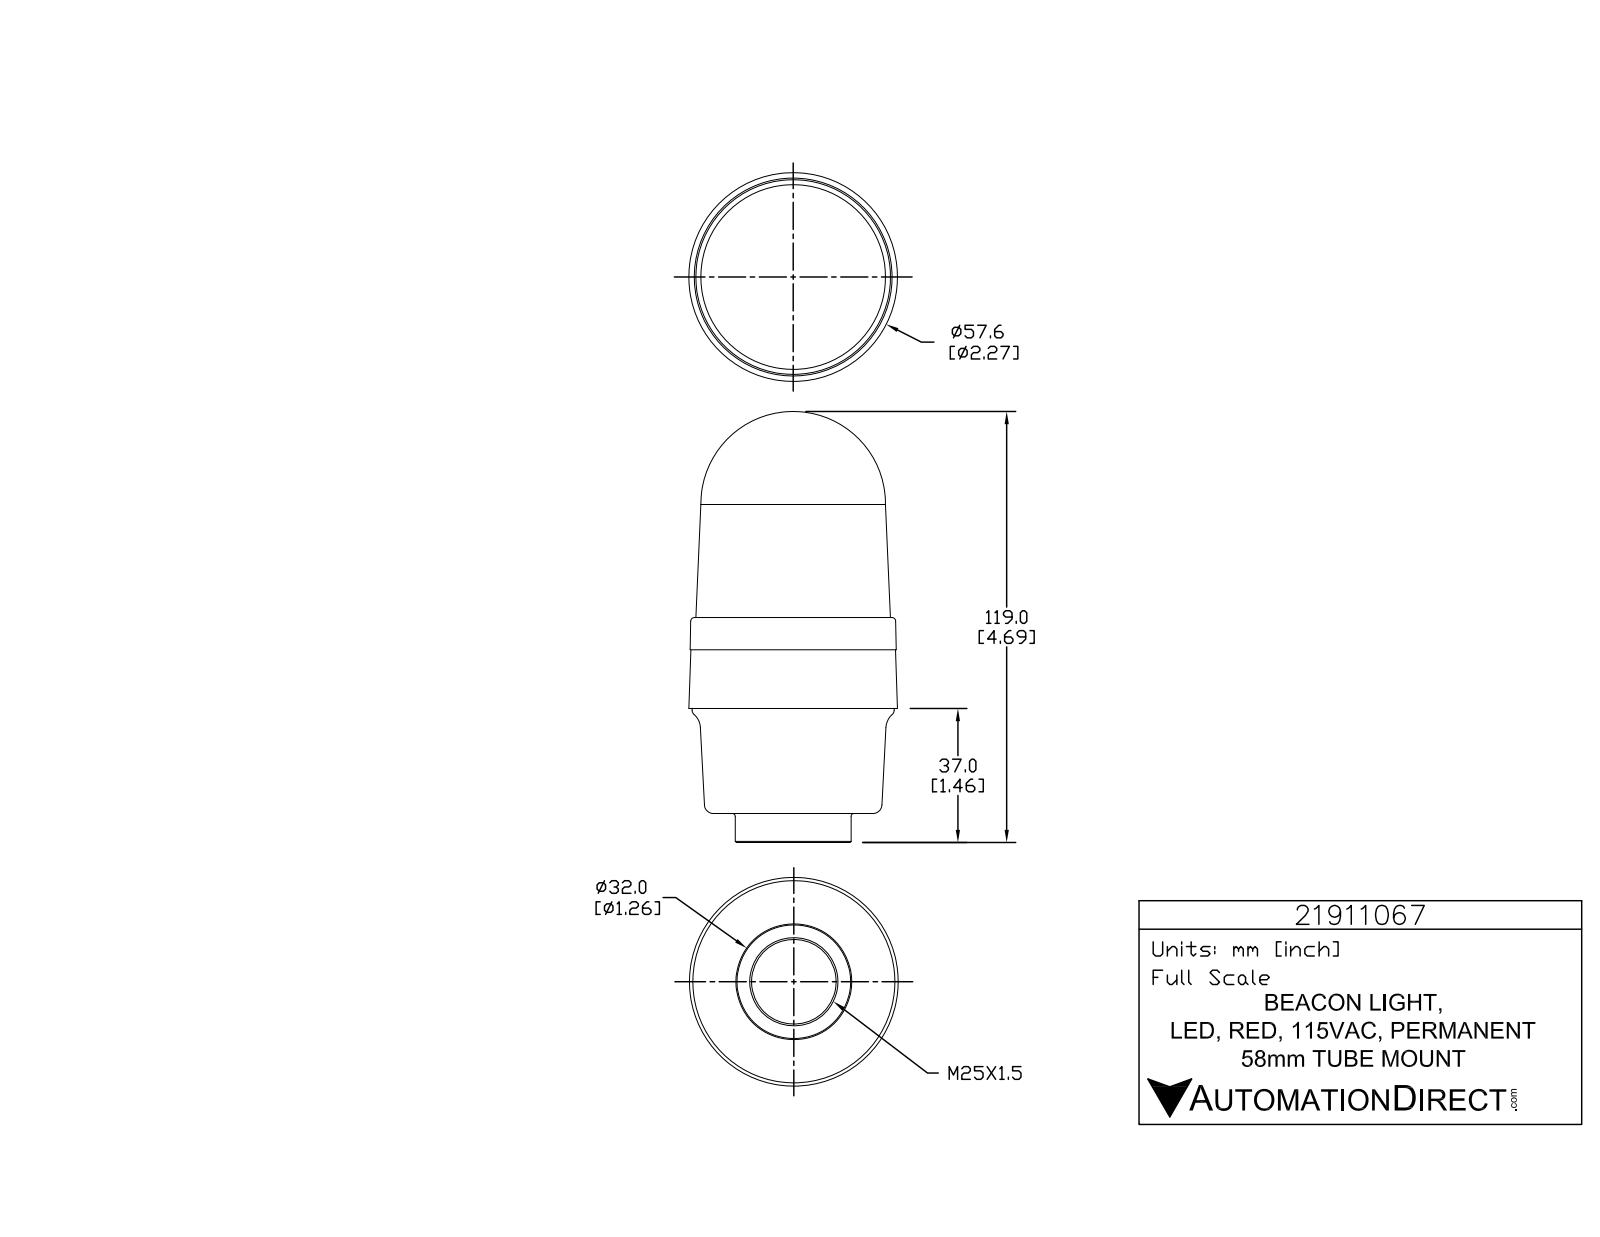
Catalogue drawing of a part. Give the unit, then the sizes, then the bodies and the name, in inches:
Units: inches
Overall size (bounding box): 4.685 × 2.269 × 2.269
Round holes (diameter × count): ⌀0.039 ×3, ⌀0.92 ×1
Round bosses / shafts (diameter × count): ⌀0.226 ×3, ⌀0.056 ×3, ⌀2.197 ×1, ⌀1.26 ×1
Partial cylindrical surfaces — rounded edges, fillets, slot ends (radius × count): R0.008 ×6, R0.008 ×6, R0.008 ×6, R0.131 ×6, R0.004 ×3, R0.005 ×3, R0.008 ×3, R0.008 ×3
Main face-to-face distances: 0.315, 1.142, 1.457, 0.988, 2.13, 2.445, 0.35, 0.638, 1.78, 2.094
Volume: 13.89 in³ · Surface area: 34.06 in²
Bodies: 1 solid, 791 faces (525 planar, 168 cylindrical, 98 other)
Part name (STEP PRODUCT): 21911067
STEP written by: SolidWorks 2015 (AUTOMOTIVE_DESIGN)
